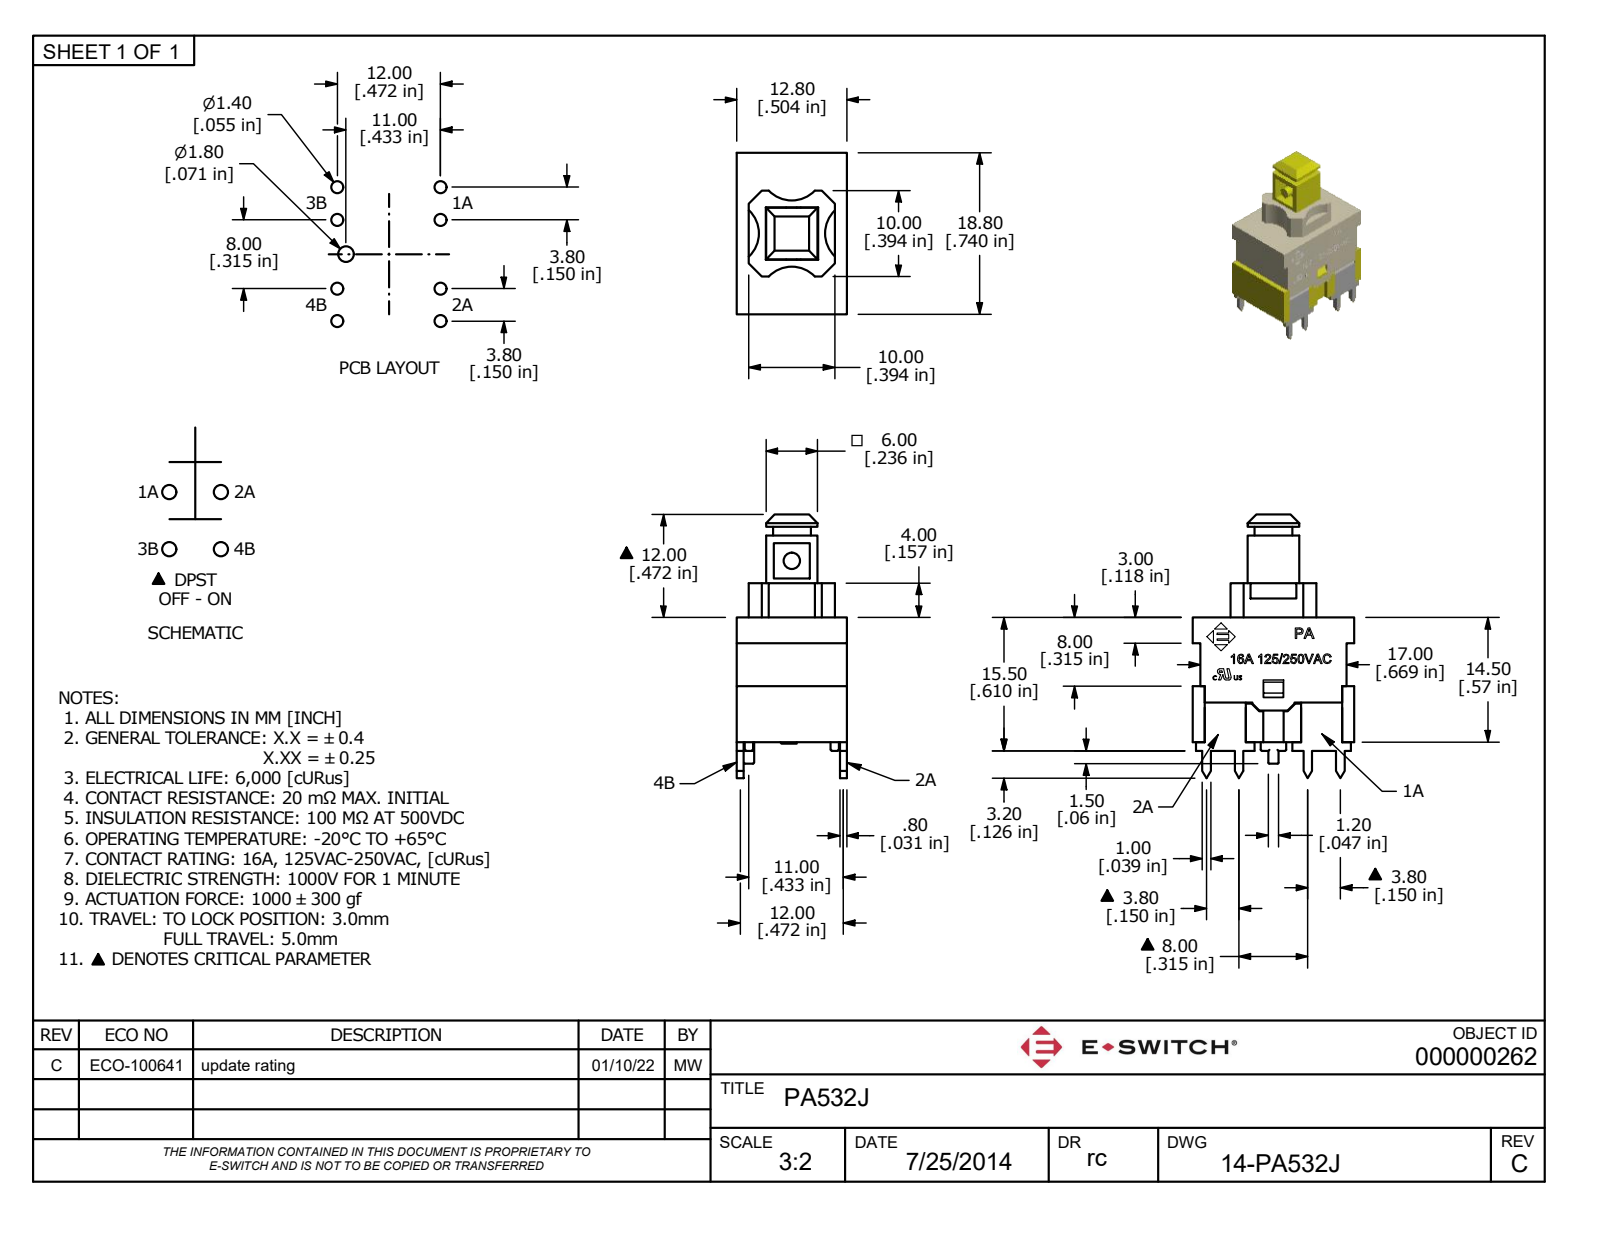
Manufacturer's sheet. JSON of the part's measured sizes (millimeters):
{"part_name": "PA532J", "step_written_by": "Autodesk Inventor 2022 (AUTOMOTIVE_DESIGN)", "units": "millimeters", "bodies": {"solids": 1, "faces": 869, "planar": 656, "cylindrical": 82, "other": 131}, "overall_size": [30.7, 18.8, 12.8], "volume_mm3": 2202, "surface_area_mm2": 4387, "round_holes": [[1.2, 2], [3, 1]], "round_bosses_or_shafts": [[0.95, 4], [2.5, 2], [1.9, 1]], "partial_cylinders_radius": [[0.25, 22], [0.12, 16], [0.15, 8], [1, 5], [3.71, 4], [0.5, 1], [0.6, 1], [1.79, 1]], "face_to_face_distances": [0.8, 12, 0.9, 16.8, 12.8, 2, 1.1, 8.6, 4.4, 1], "hole_center_spacings": [11.8]}
